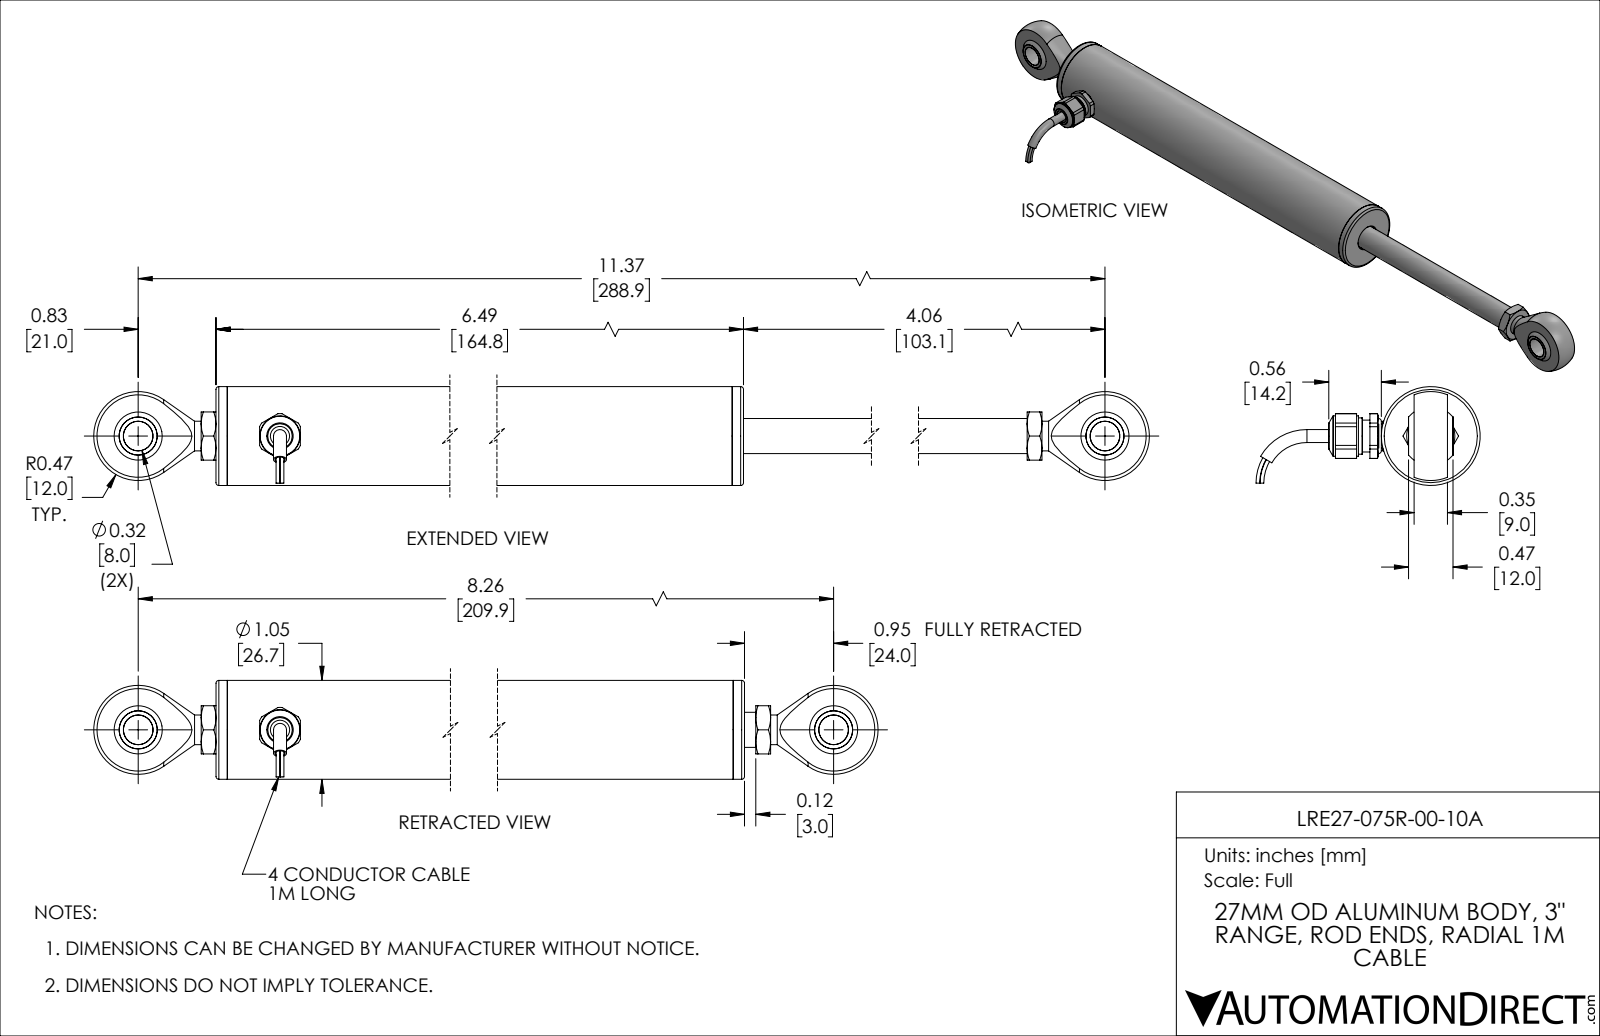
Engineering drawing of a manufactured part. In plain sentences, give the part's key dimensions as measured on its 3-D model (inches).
The part is named "LRE27-075R-00-10A". Its 3-D file was written by "SolidWorks 2019 (AUTOMOTIVE_DESIGN)". It is 17 solids with 225 faces: 82 planar, 57 cylindrical and 86 other. Overall it measures 9.208 by 2.382 by 1.05 inches. Its volume is 3.686 cubic inches and its surface area 73.99 square inches. Round holes: 2 of diameter 0.268, 2 of diameter 0.315, 1 of diameter 0.106, 1 of diameter 0.138, 1 of diameter 0.201, 1 of diameter 0.205, 1 of diameter 0.25, 1 of diameter 0.274, 1 of diameter 0.36, 1 of diameter 0.375, 1 of diameter 0.386, 1 of diameter 0.499. Round bosses or shafts: 4 of diameter 0.039, 2 of diameter 0.315, 1 of diameter 1.05, 1 of diameter 0.848, 1 of diameter 0.5, 1 of diameter 0.429, 1 of diameter 0.386, 1 of diameter 0.373. Partial cylindrical surfaces (rounded edges, fillets, slot ends): 1 of radius 0.238. The main face-to-face distances are 0.12, 6.37, 0.354, 6.49, 6.25, 0.4, 0.28, 5.97, 6.09, 0.157. The hole center spacings are 1.507, 6.757, 8.264.
